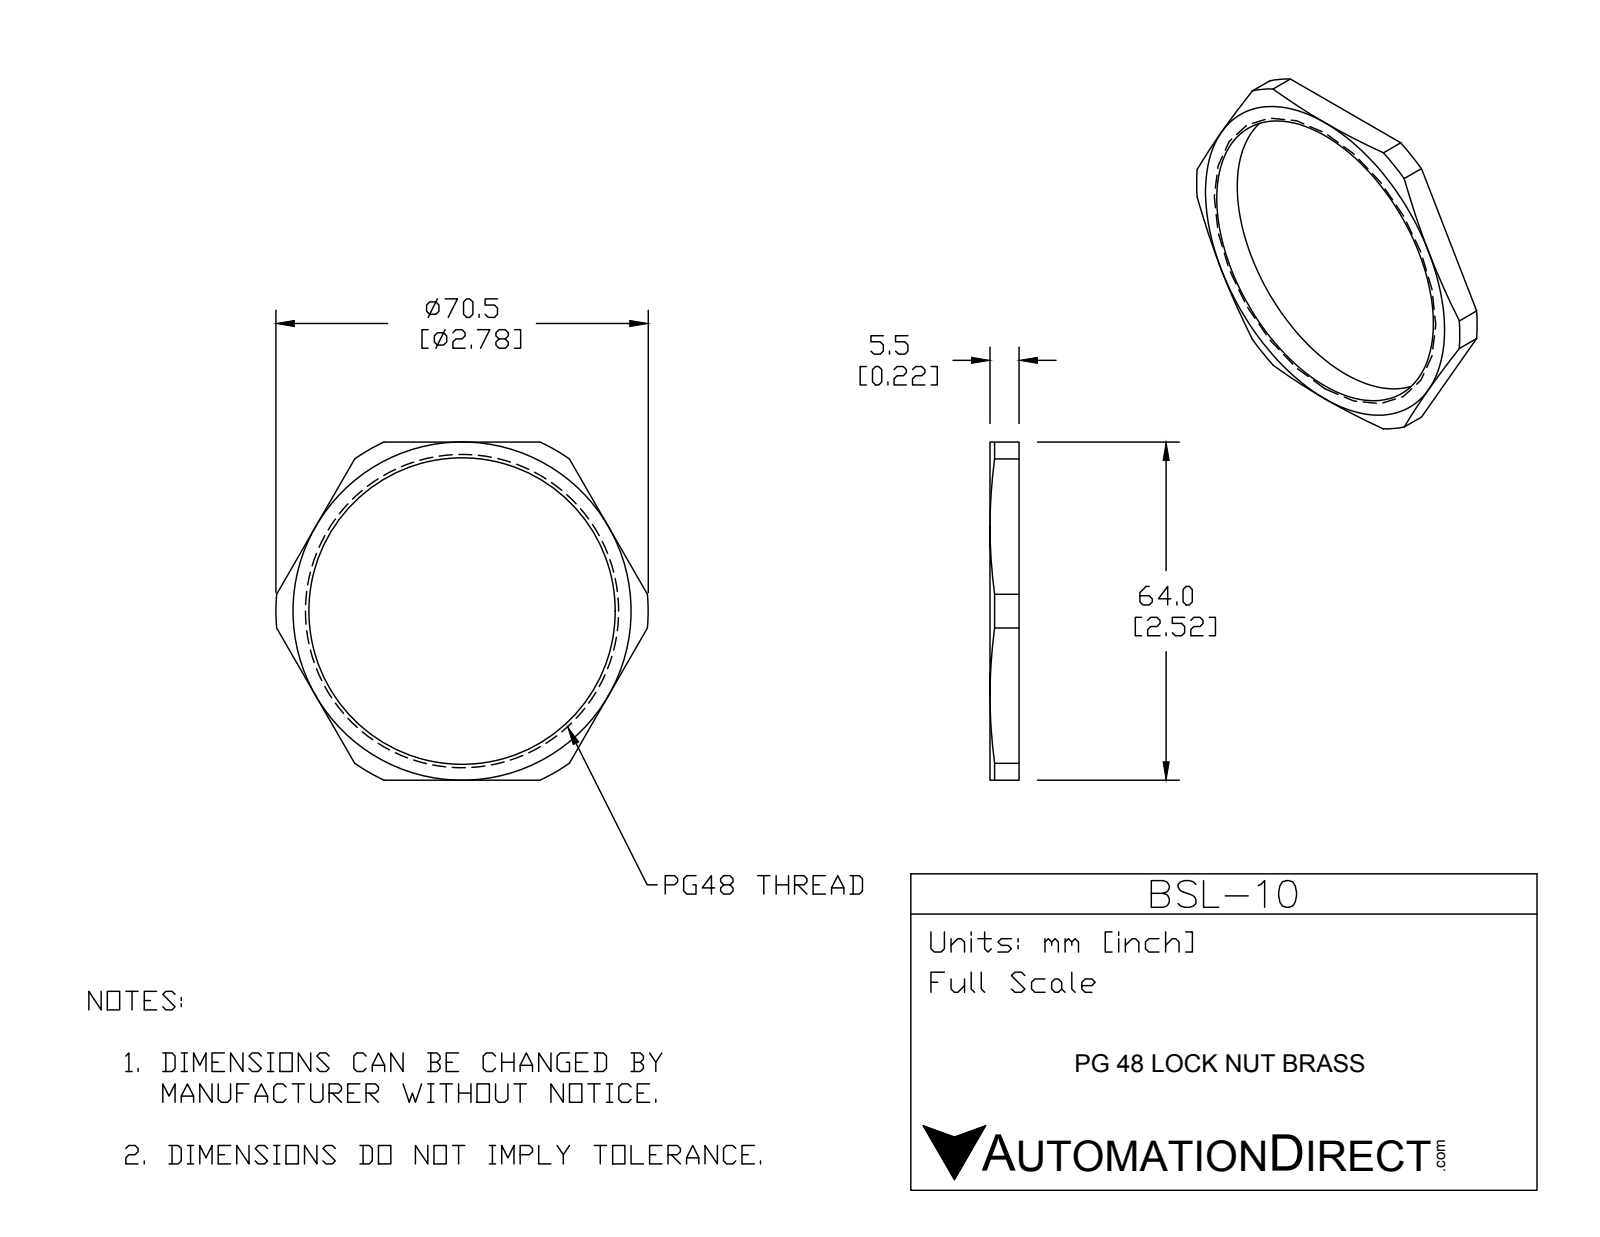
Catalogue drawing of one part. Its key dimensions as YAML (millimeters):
part_name: "BSL-10"
step_written_by: "SolidWorks 2015 (CONFIG_CONTROL_DESIGN)"
units: millimeters
bodies: {solids: 1, faces: 23, planar: 8, cylindrical: 9, other: 6}
overall_size: [70.5, 64, 5.5]
volume: 4704
surface_area: 3861
round_holes:
  - {diameter: 58, count: 1}
partial_cylinders:
  - {radius: 35.25, count: 1}
face_to_face_distances: [5.5, 64]
